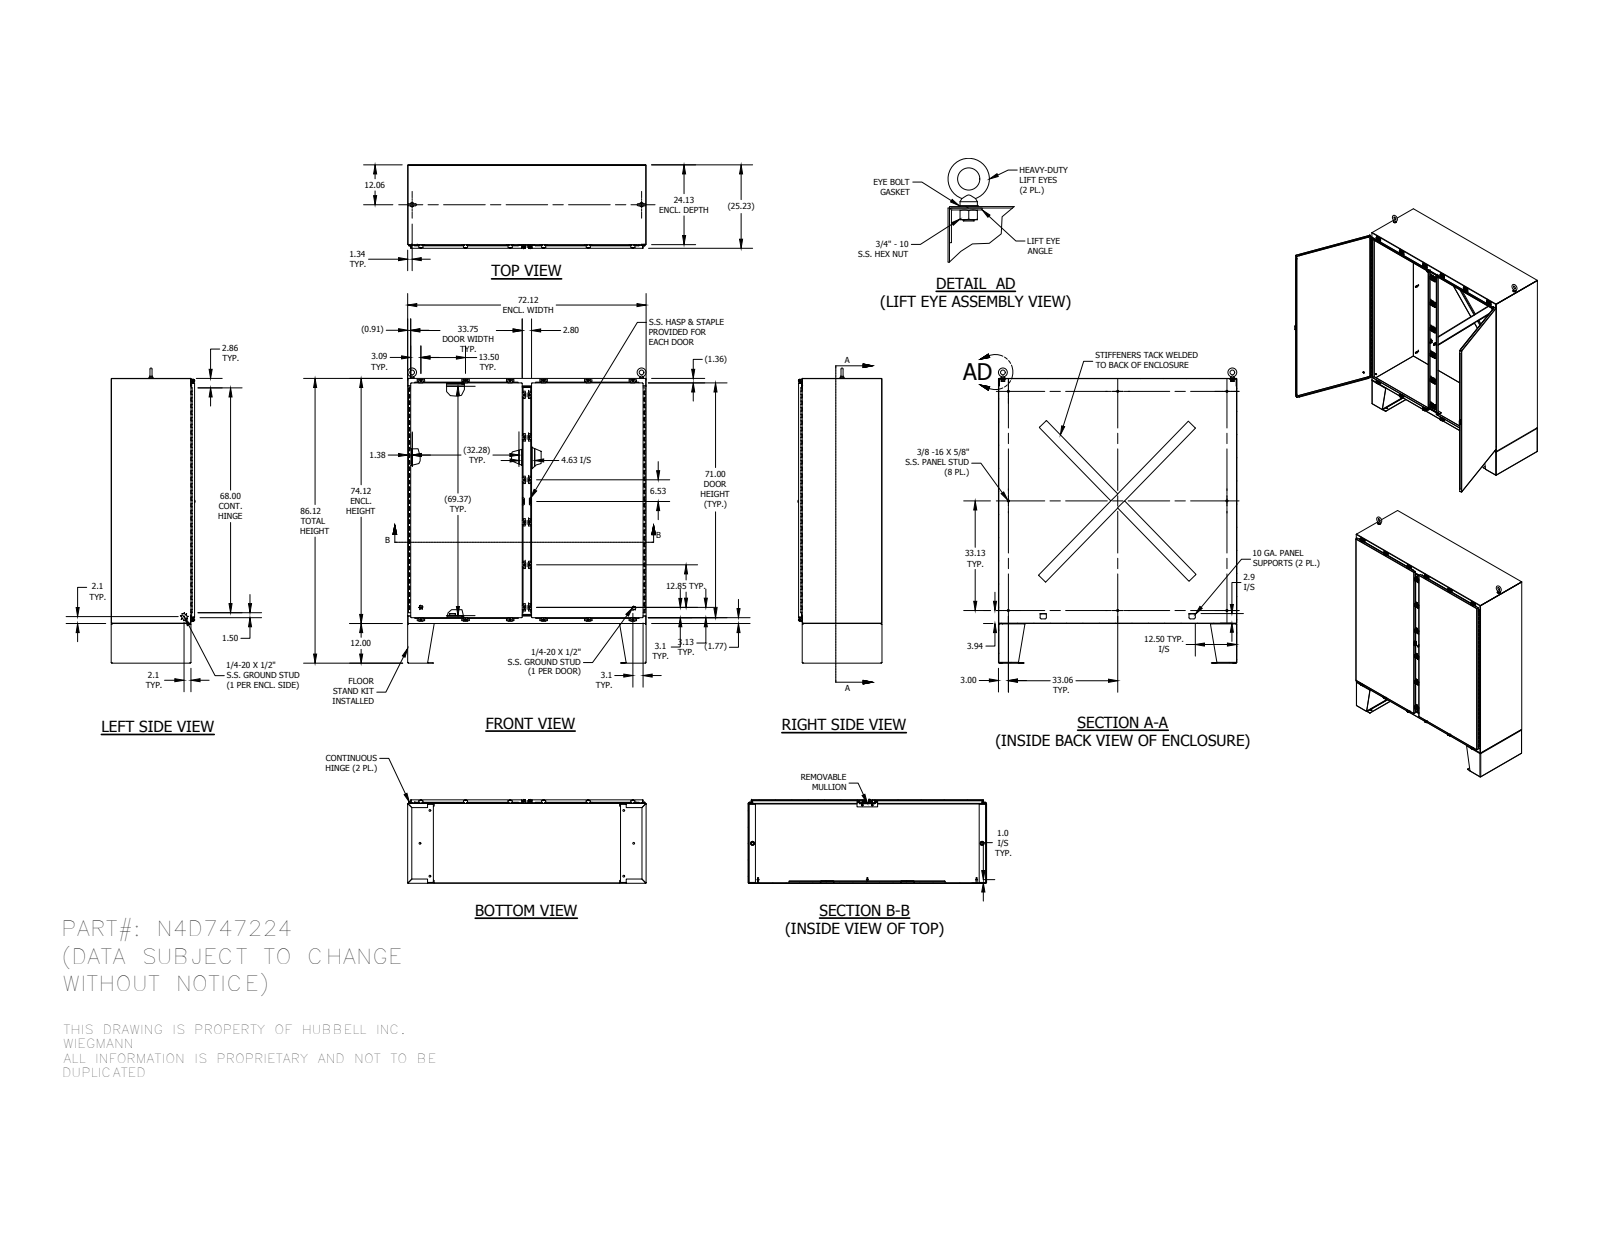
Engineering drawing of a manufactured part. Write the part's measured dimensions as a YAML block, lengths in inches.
part_name: "38626_1; N4D7472FB_1; N4D7424LRS_1; 328131-68_1_1 (+8 more)"
step_written_by: "SolidWorks 2014 (AUTOMOTIVE_DESIGN)"
units: inches
bodies: {solids: 185, faces: 6996, planar: 2802, cylindrical: 2798, other: 1396}
overall_size: [89.248, 72.125, 25.355]
volume: 2069
surface_area: 43533
round_holes:
  - {diameter: 0.11, count: 48}
  - {diameter: 0.211, count: 24}
  - {diameter: 0.281, count: 24}
  - {diameter: 0.3, count: 24}
  - {diameter: 0.563, count: 18}
  - {diameter: 0.375, count: 16}
  - {diameter: 0.196, count: 4}
  - {diameter: 0.201, count: 4}
  - {diameter: 0.312, count: 4}
  - {diameter: 0.313, count: 4}
  - {diameter: 0.142, count: 2}
  - {diameter: 0.156, count: 2}
round_bosses_or_shafts:
  - {diameter: 0.25, count: 31}
  - {diameter: 0.52, count: 24}
  - {diameter: 0.5, count: 24}
  - {diameter: 0.35, count: 24}
  - {diameter: 0.33, count: 10}
  - {diameter: 0.625, count: 8}
  - {diameter: 0.438, count: 4}
  - {diameter: 0.337, count: 3}
partial_cylinders:
  - {radius: 0.03, count: 268}
  - {radius: 0.125, count: 56}
  - {radius: 0.141, count: 48}
  - {radius: 0.25, count: 39}
  - {radius: 0.062, count: 34}
  - {radius: 0.1, count: 24}
  - {radius: 0.094, count: 22}
  - {radius: 0.219, count: 22}
face_to_face_distances: [0.094, 25.133, 25.039, 25.227, 72.031, 74.031, 72.125, 24.031, 1.102, 71.938]
hole_center_spacings: [13.5, 72.977, 0.876, 1.625, 36.314, 37.125, 37.939, 71.717]
